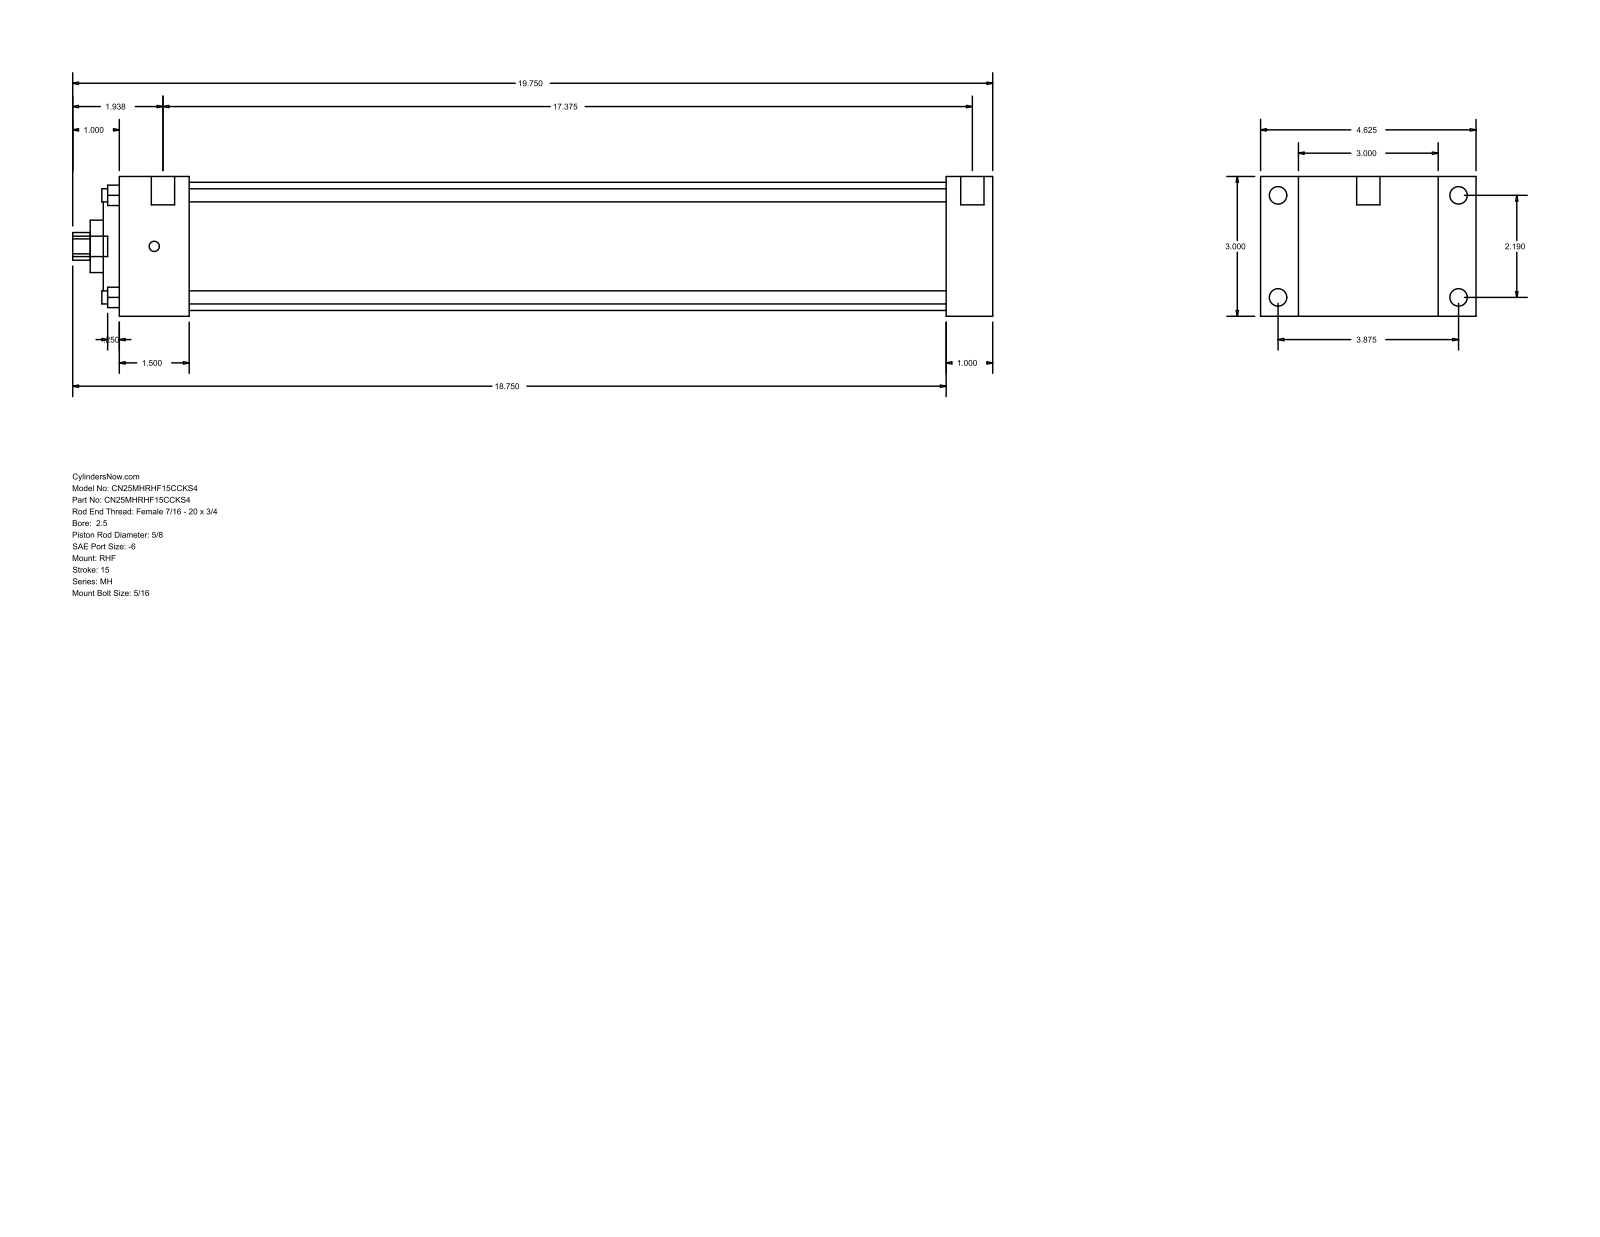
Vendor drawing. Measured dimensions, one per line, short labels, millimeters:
name: MH_RHF__0250_0.625
written by: GSSL Pune (CONFIG_CONTROL_DESIGN)
unit: mm
bodies: 0 solids, 90 faces (61 planar, 29 cylindrical, 0 other)
size: 501.65 × 117.47 × 76.2
holes: 4× ⌀7.14, 1× ⌀15.88, 1× ⌀28.57, 1× ⌀55.55, 1× ⌀69.85
bosses: 4× ⌀9.53, 4× ⌀5.56, 2× ⌀12.7, 1× ⌀11.11
rounds: 1× R7.54
face distances: 76.2, 25.4, 20.64, 96.84, 476.25, 450.85, 117.48, 38.1, 412.75, 438.15
hole spacings: 39.33, 55.62, 78.66
